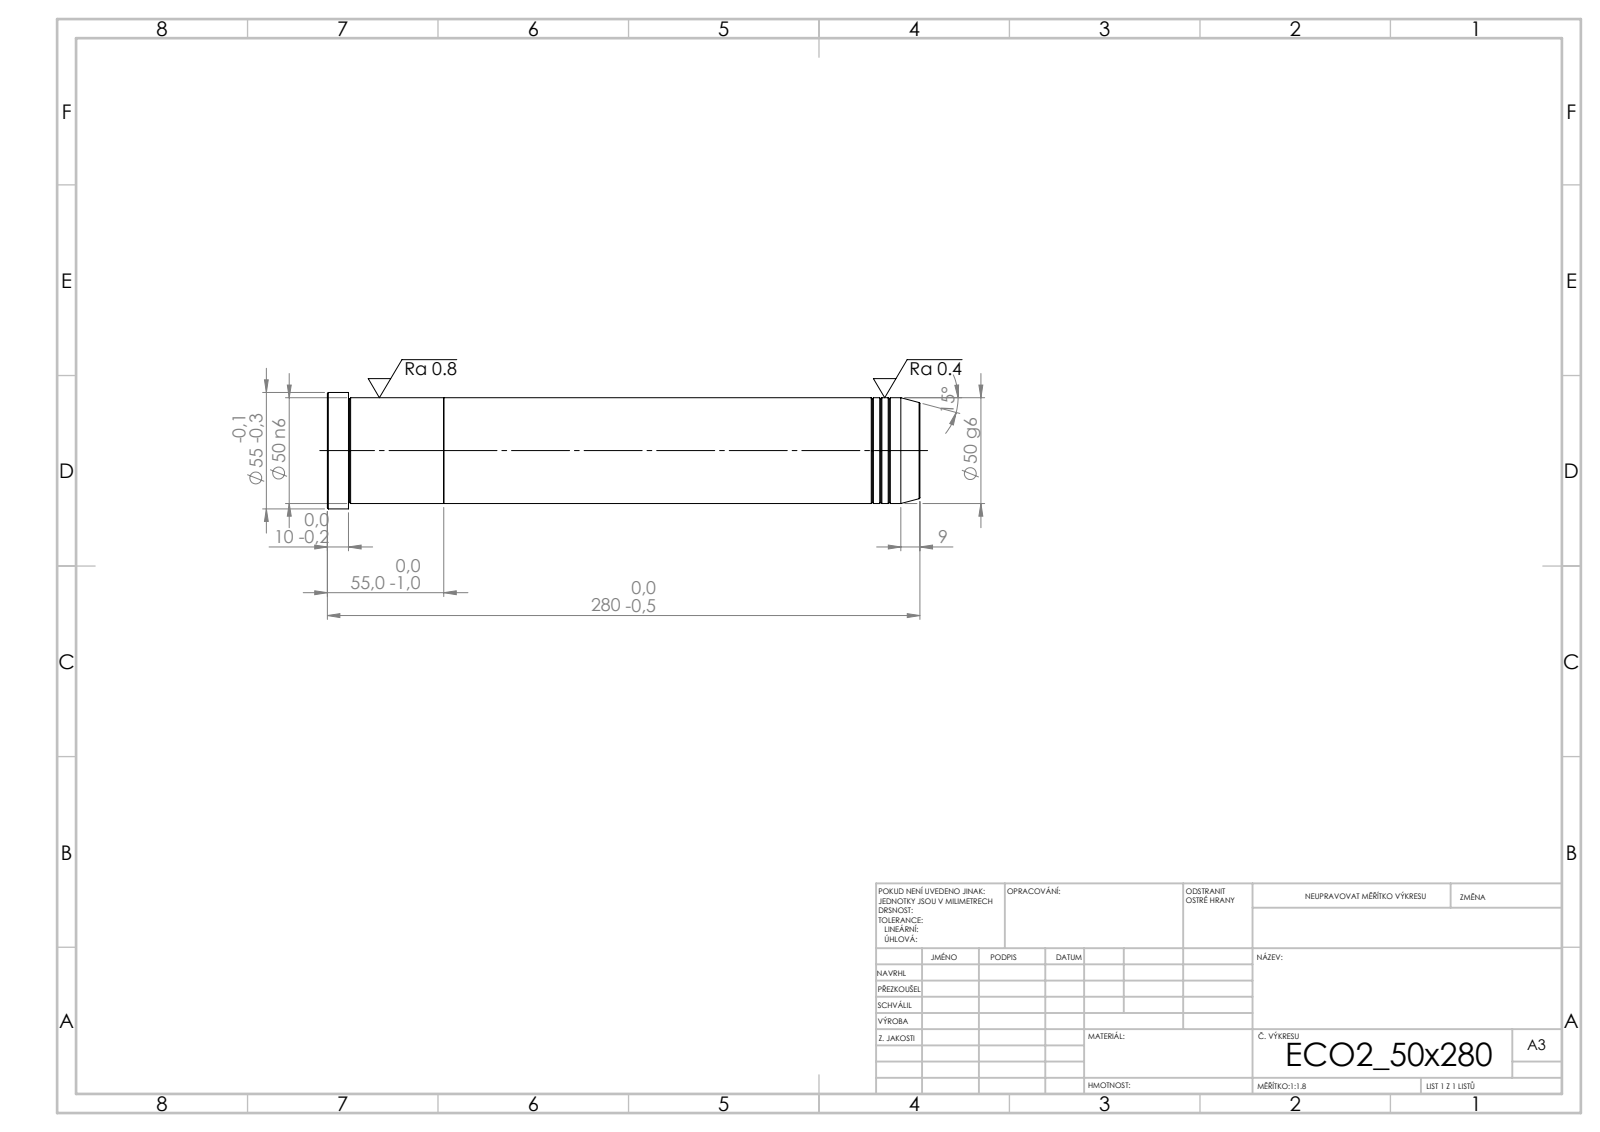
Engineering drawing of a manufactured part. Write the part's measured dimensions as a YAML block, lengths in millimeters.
step_written_by: "SolidWorks 2019 (CONFIG_CONTROL_DESIGN)"
units: millimeters
bodies: {solids: 2, faces: 39, planar: 5, cylindrical: 12, other: 22}
overall_size: [280, 55, 55]
volume: 551982
surface_area: 52716
round_bosses_or_shafts:
  - {diameter: 55, count: 1}
  - {diameter: 50, count: 1}
face_to_face_distances: [55, 225, 280, 270, 45, 10]
